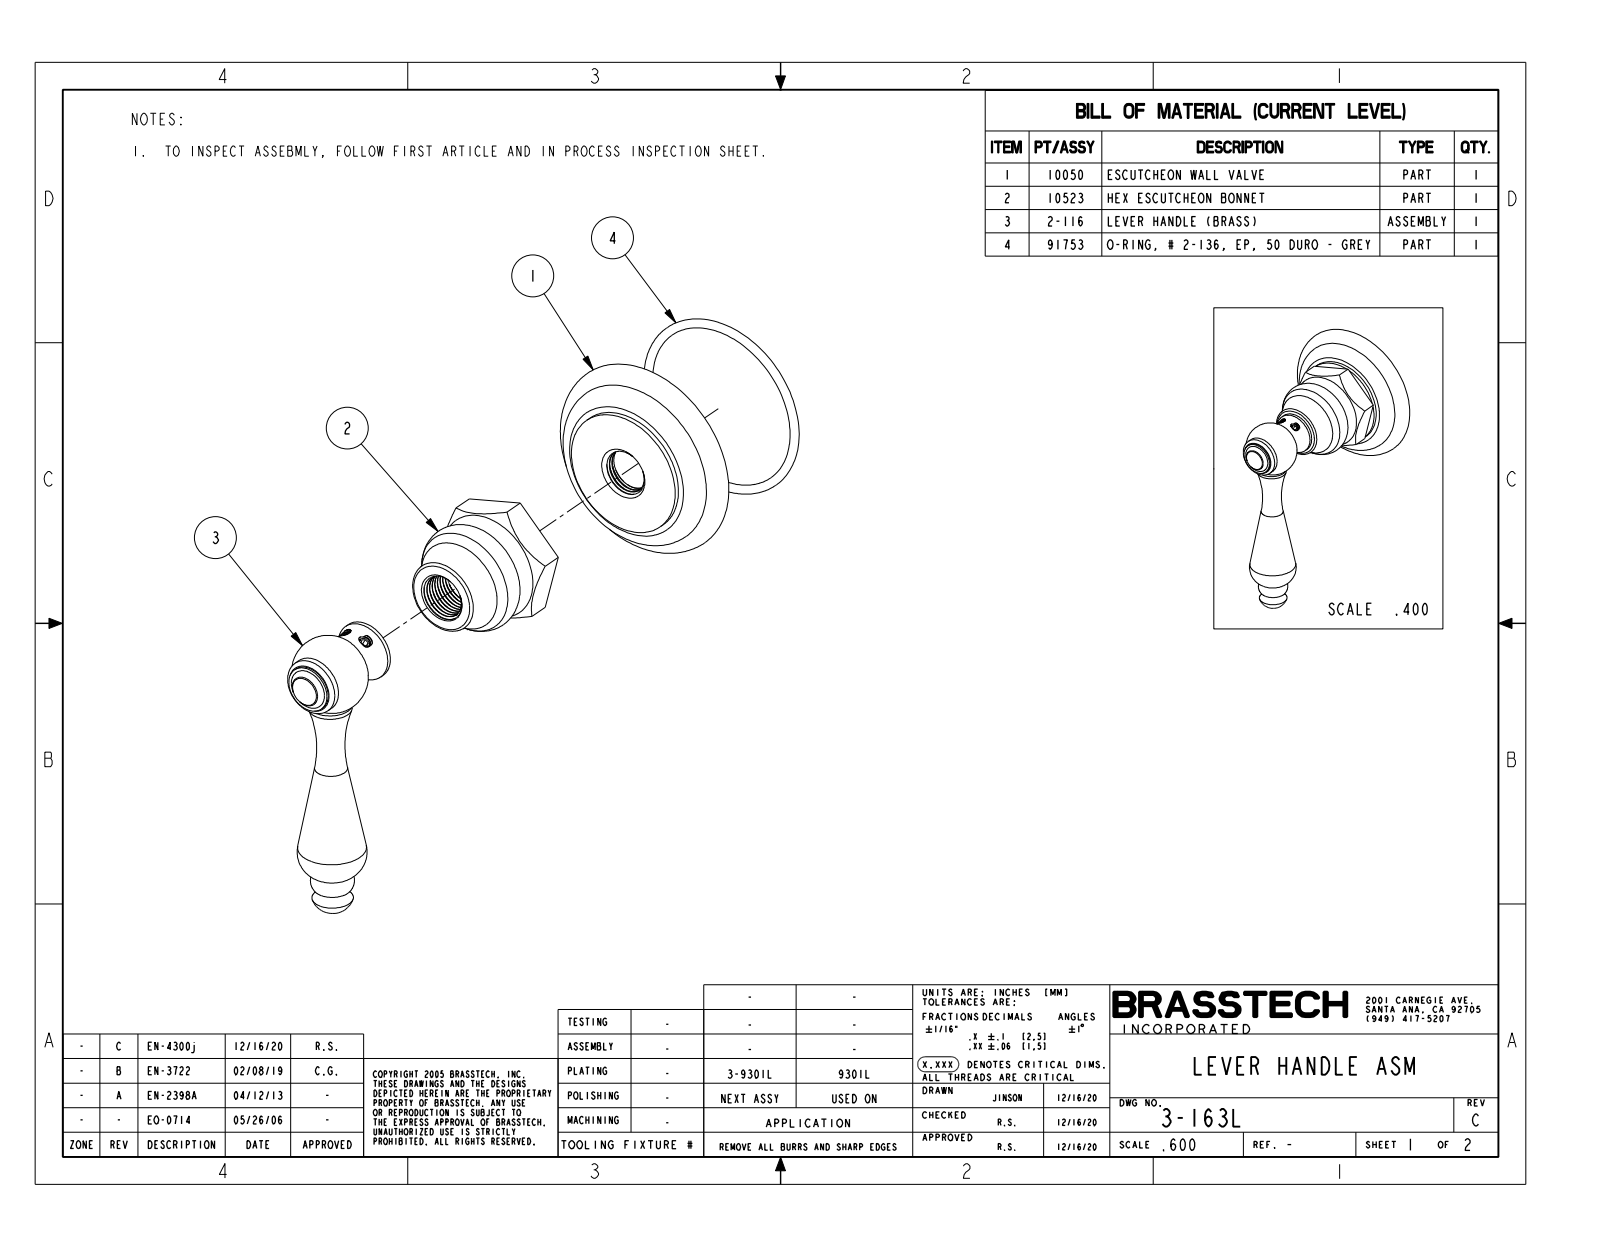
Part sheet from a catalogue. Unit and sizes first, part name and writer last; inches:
Units: inches
Overall size (bounding box): 3.471 × 3.471 × 2.872
Round bosses / shafts (diameter × count): ⌀1.482 ×1, ⌀0.705 ×1, ⌀0.661 ×1, ⌀0.544 ×1, ⌀0.5 ×1, ⌀0.4 ×1
Main face-to-face distances: 1.313, 1.687, 0.375, 1.312, 1.702, 1.327, 0.015, 1.313, 0.437, 0.062
Volume: 3.927 in³ · Surface area: 22.42 in²
Bodies: 1 solid, 79 faces (27 planar, 12 cylindrical, 40 other)
Part name (STEP PRODUCT): 3-163L
STEP written by: CREO PARAMETRIC BY PTC INC, 2018400 (CONFIG_CONTROL_DESIGN)
